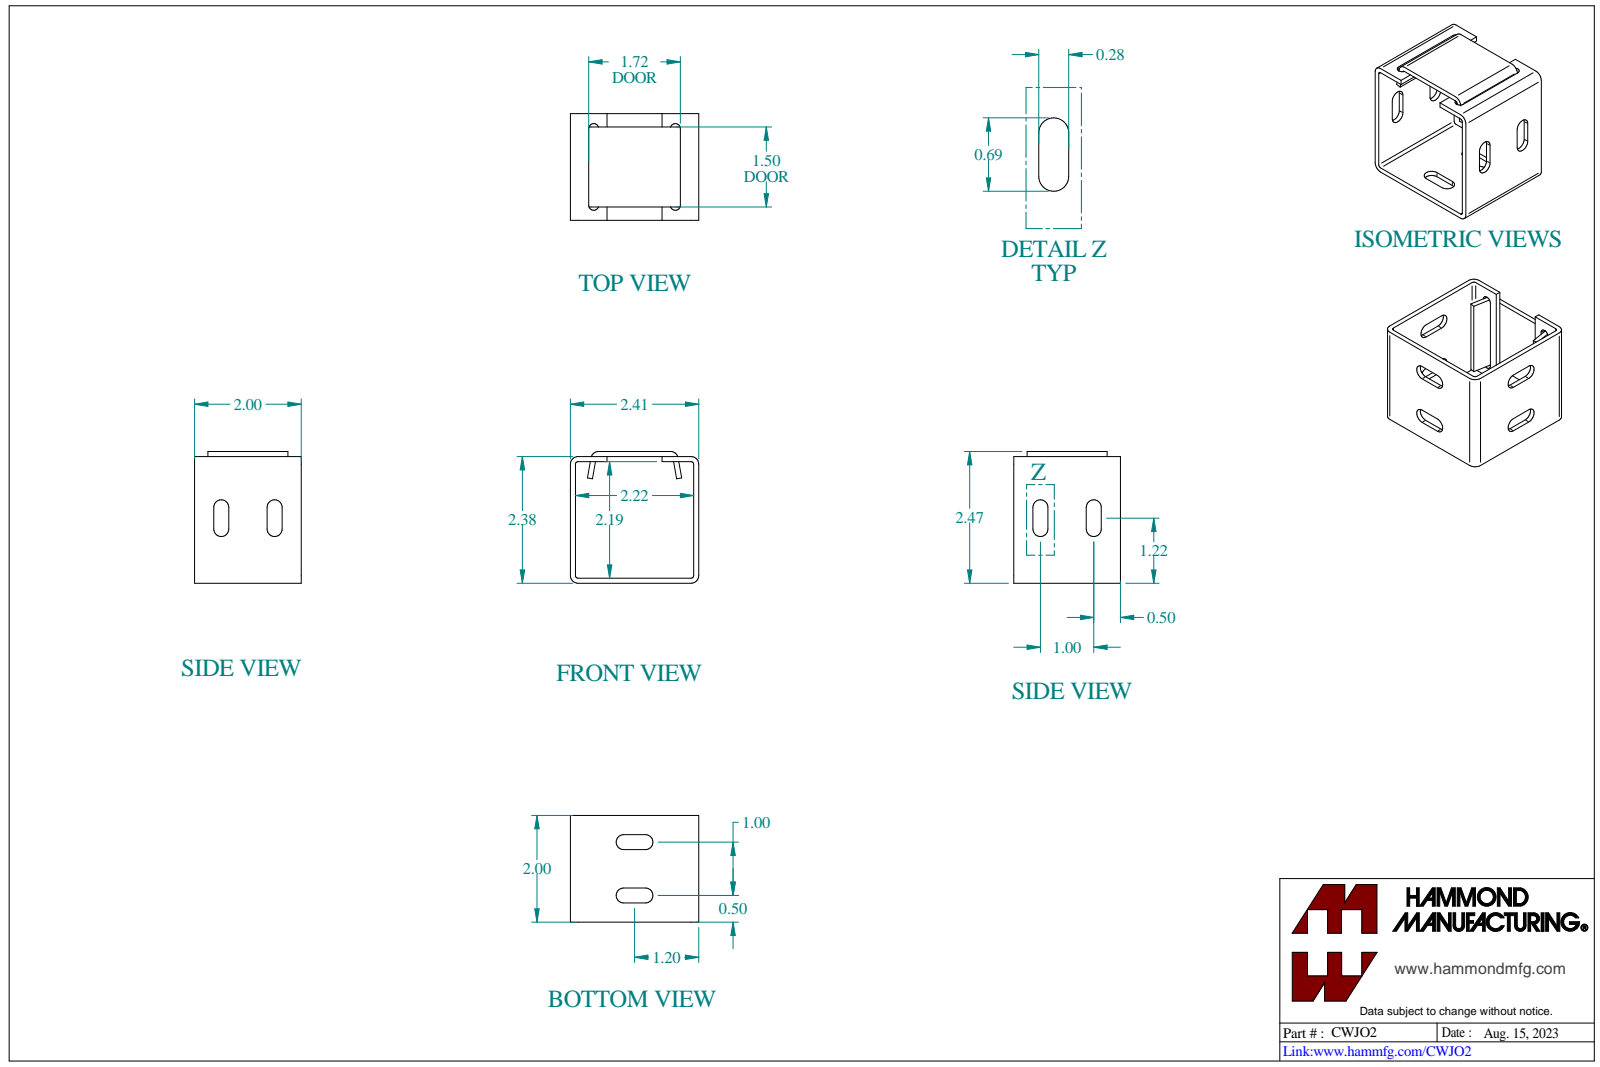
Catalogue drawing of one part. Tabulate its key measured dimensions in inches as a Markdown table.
| quantity | value |
| --- | --- |
| part name | CWJO2 |
| STEP written by | SolidWorks 2023 (CONFIG_CONTROL_DESIGN) |
| units | inches |
| bodies | 2 solids, 74 faces (40 planar, 34 cylindrical, 0 other) |
| overall size | 2.47 × 2.406 × 2 |
| volume | 1.7 in³ |
| surface area | 40.05 in² |
| partial cylindrical surfaces (radius × count) | 0.048 × 6, 0.143 × 6, 0.094 × 4, 0.141 × 4, 0.141 × 4 |
| main face-to-face distances | 0.095, 2.311, 0.095, 2.28, 2.406, 2.216, 2.375, 2.47, 2.375, 2.185 |
